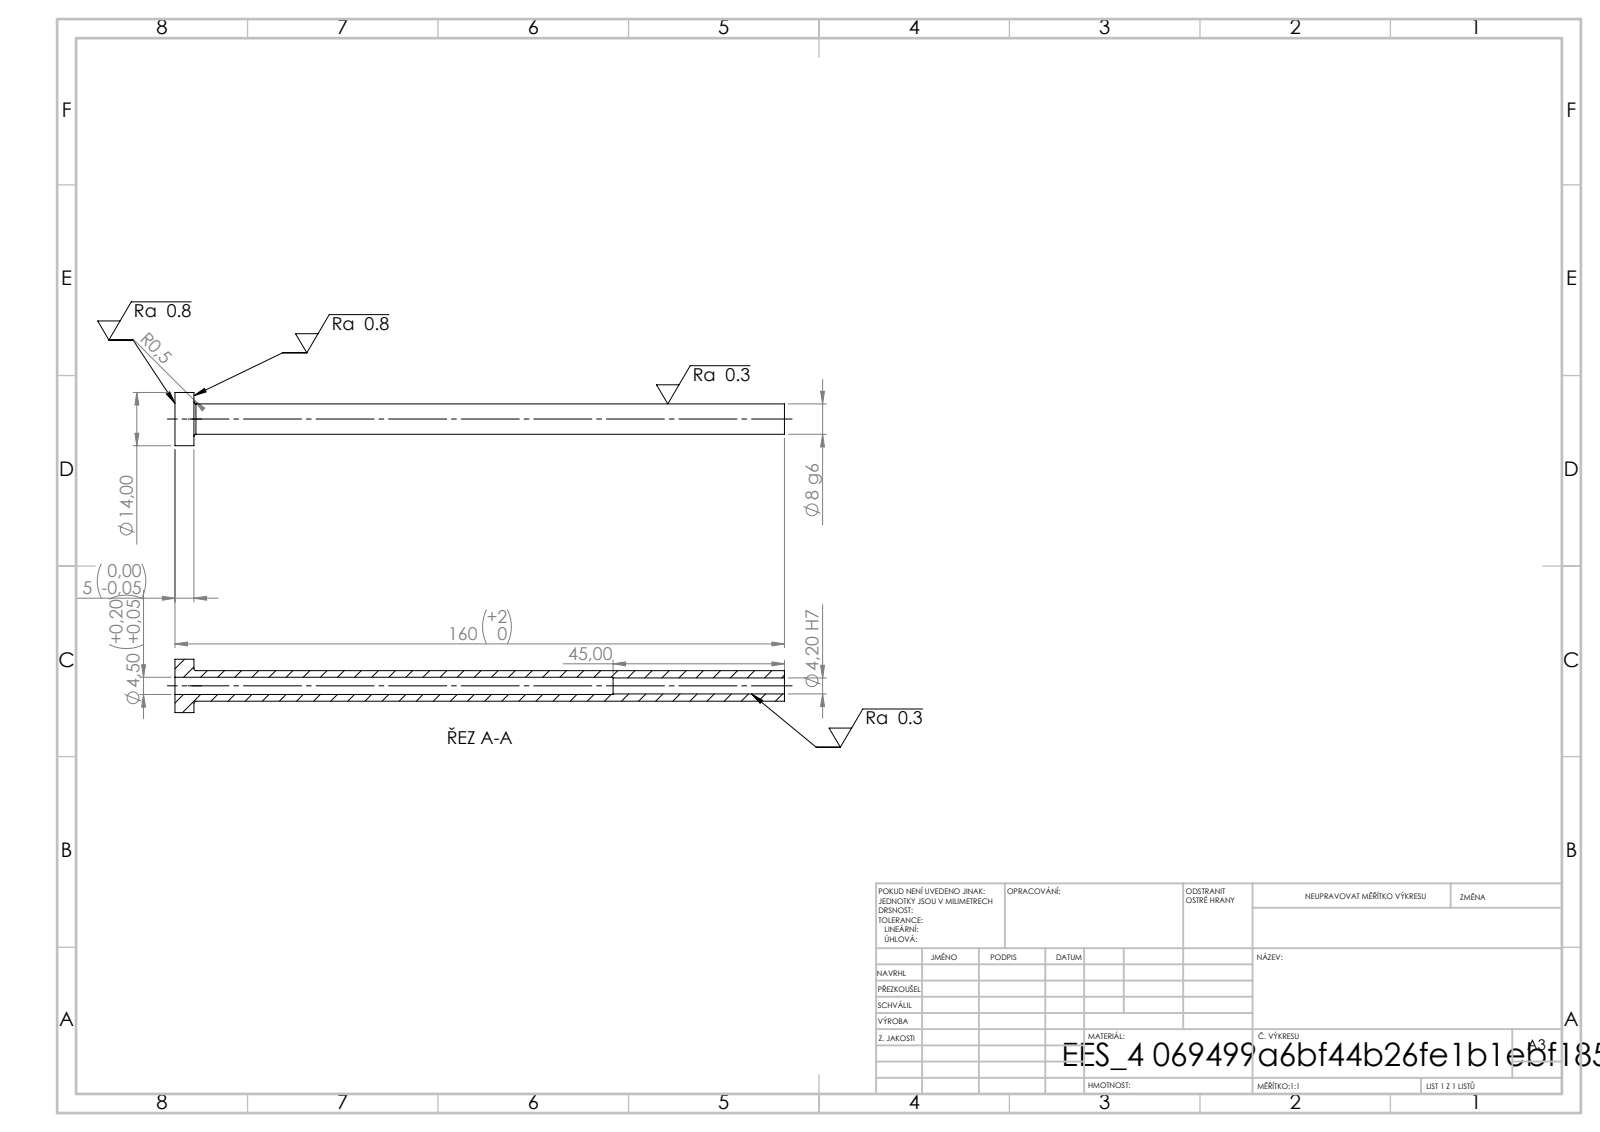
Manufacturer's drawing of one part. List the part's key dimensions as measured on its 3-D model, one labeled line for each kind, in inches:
STEP written by: SolidWorks 2019 (CONFIG_CONTROL_DESIGN)
Units: inches
Bodies: 1 solid, 14 faces (4 planar, 8 cylindrical, 2 other)
Overall size (bounding box): 6.299 × 0.551 × 0.551
Volume: 0.373 in³ · Surface area: 10.25 in²
Round holes (diameter × count): ⌀0.165 ×1, ⌀0.177 ×1
Round bosses / shafts (diameter × count): ⌀0.551 ×1, ⌀0.315 ×1
Main face-to-face distances: 0.197, 6.299, 6.102, 4.528, 4.331, 1.772
